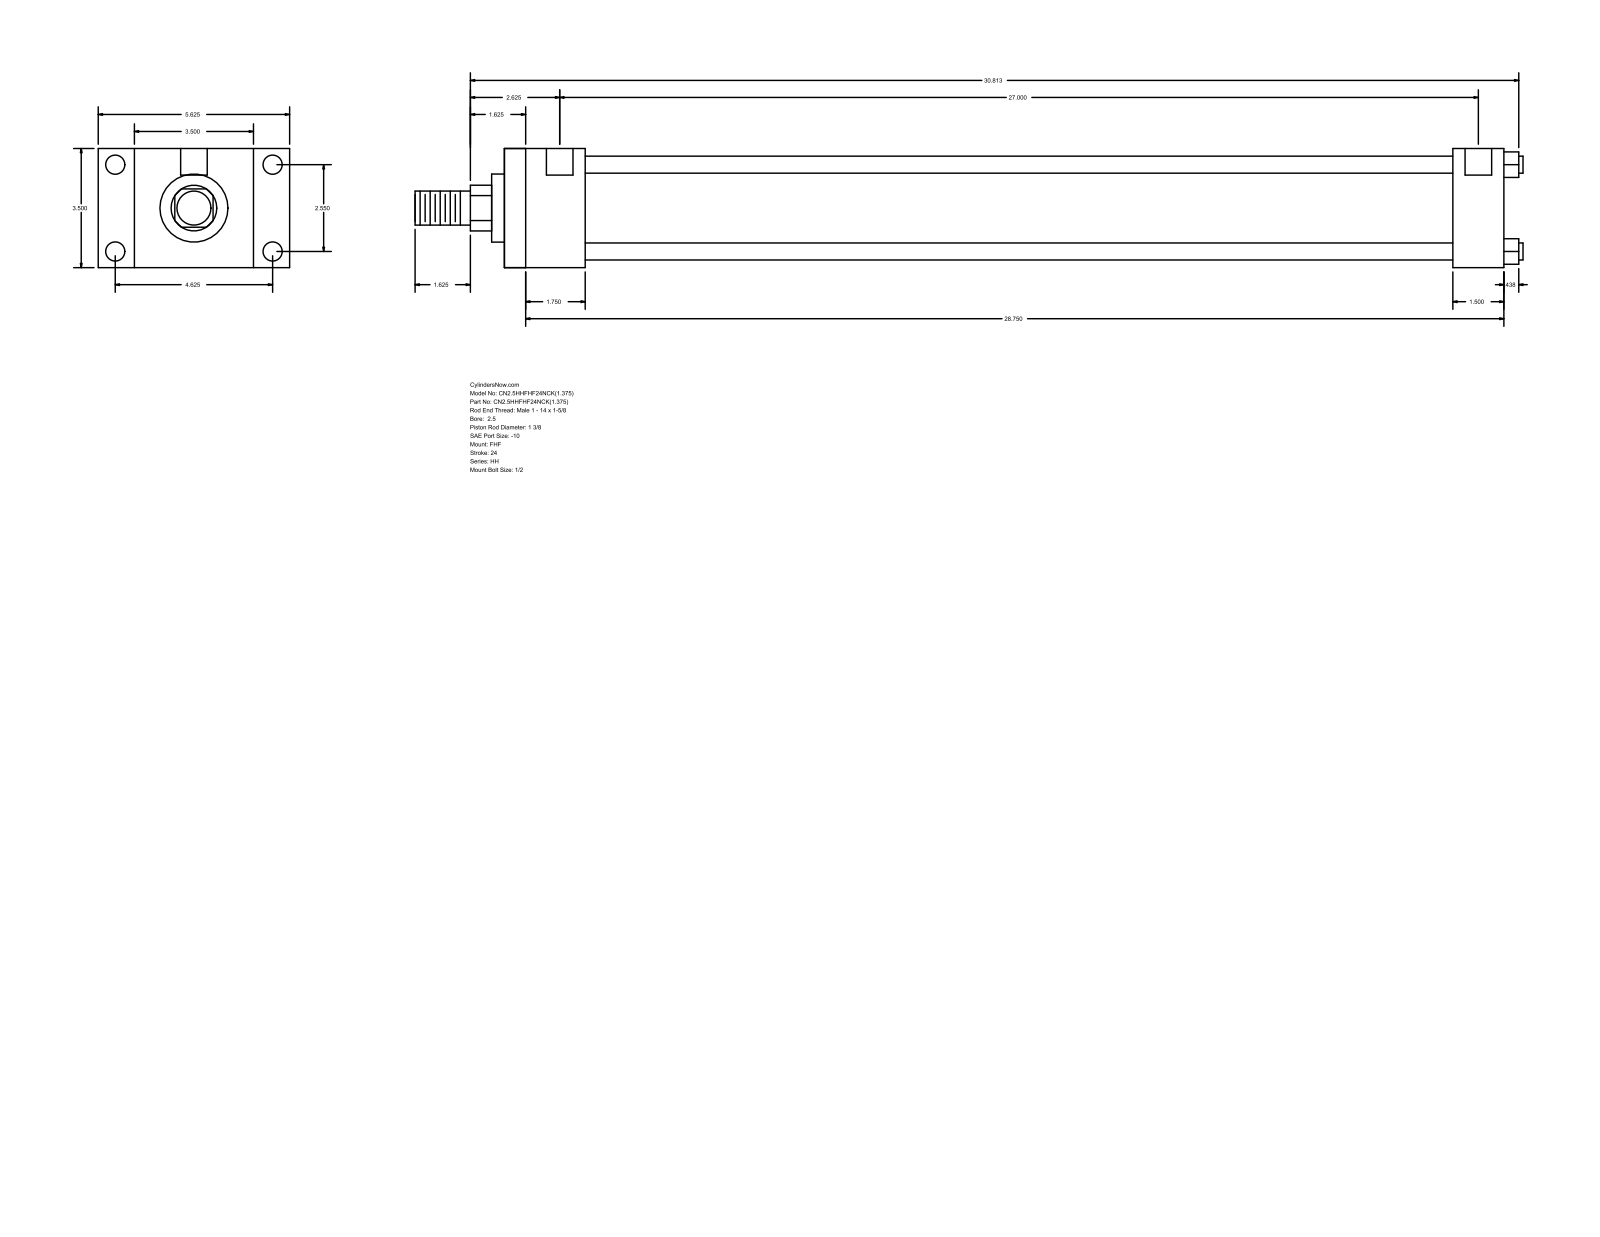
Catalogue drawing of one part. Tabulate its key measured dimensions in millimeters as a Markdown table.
| quantity | value |
| --- | --- |
| part name | HH_FHF__0250_1.375 |
| STEP written by | GSSL Pune (CONFIG_CONTROL_DESIGN) |
| units | millimeters |
| bodies | 0 solids, 88 faces (60 planar, 28 cylindrical, 0 other) |
| overall size | 827.09 × 142.88 × 88.9 |
| round holes (diameter × count) | 5.56 × 4, 14.3 × 4, 19.84 × 2 |
| round bosses / shafts (diameter × count) | 12.7 × 4, 73.03 × 1, 50.8 × 1, 34.92 × 1, 25.4 × 1 |
| partial cylindrical surfaces (radius × count) | 17.06 × 1 |
| main face-to-face distances | 88.9, 60.32, 26.99, 115.89, 746.12, 685.8, 142.88, 708.02, 647.7, 38.1 |
| hole center spacings | 1.58, 64.76, 117.48, 134.15, 687.39, 688.97, 685.81 |
